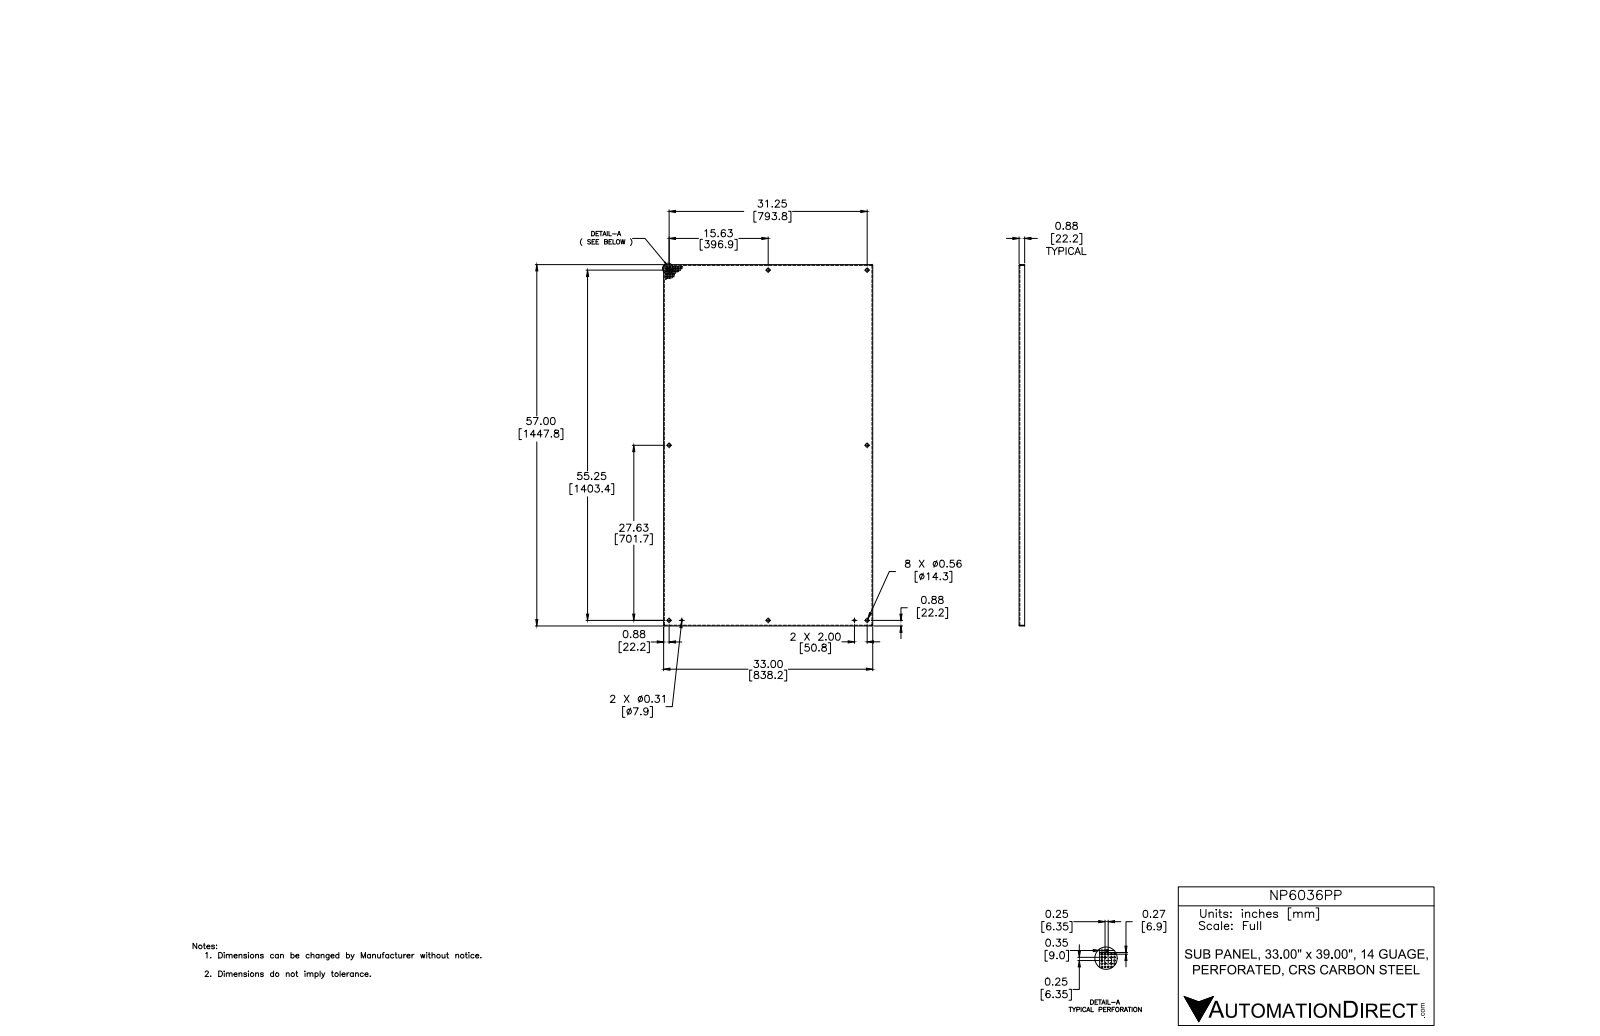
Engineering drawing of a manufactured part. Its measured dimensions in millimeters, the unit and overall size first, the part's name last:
Units: millimetres
Overall size (bounding box): 1447.8 × 838.2 × 22.23
Round holes (diameter × count): ⌀14.3 ×8, ⌀7.92 ×2
Partial cylindrical surfaces — rounded edges, fillets, slot ends (radius × count): R0.79 ×4, R2.67 ×4
Main face-to-face distances: 1.88, 836.32, 1445.92, 838.2, 834.44, 1447.8, 1444.04, 20.35, 22.23, 3.21
Hole centre spacings: 793.75, 50.8, 396.87, 396.88, 701.67, 701.68, 703.52, 742.95
Volume: 2 446 000 mm³ · Surface area: 2 612 000 mm²
Bodies: 1 solid, 48 faces (22 planar, 18 cylindrical, 8 other)
Part name (STEP PRODUCT): NP_PP
STEP written by: Autodesk Inventor 2014 (AUTOMOTIVE_DESIGN)
